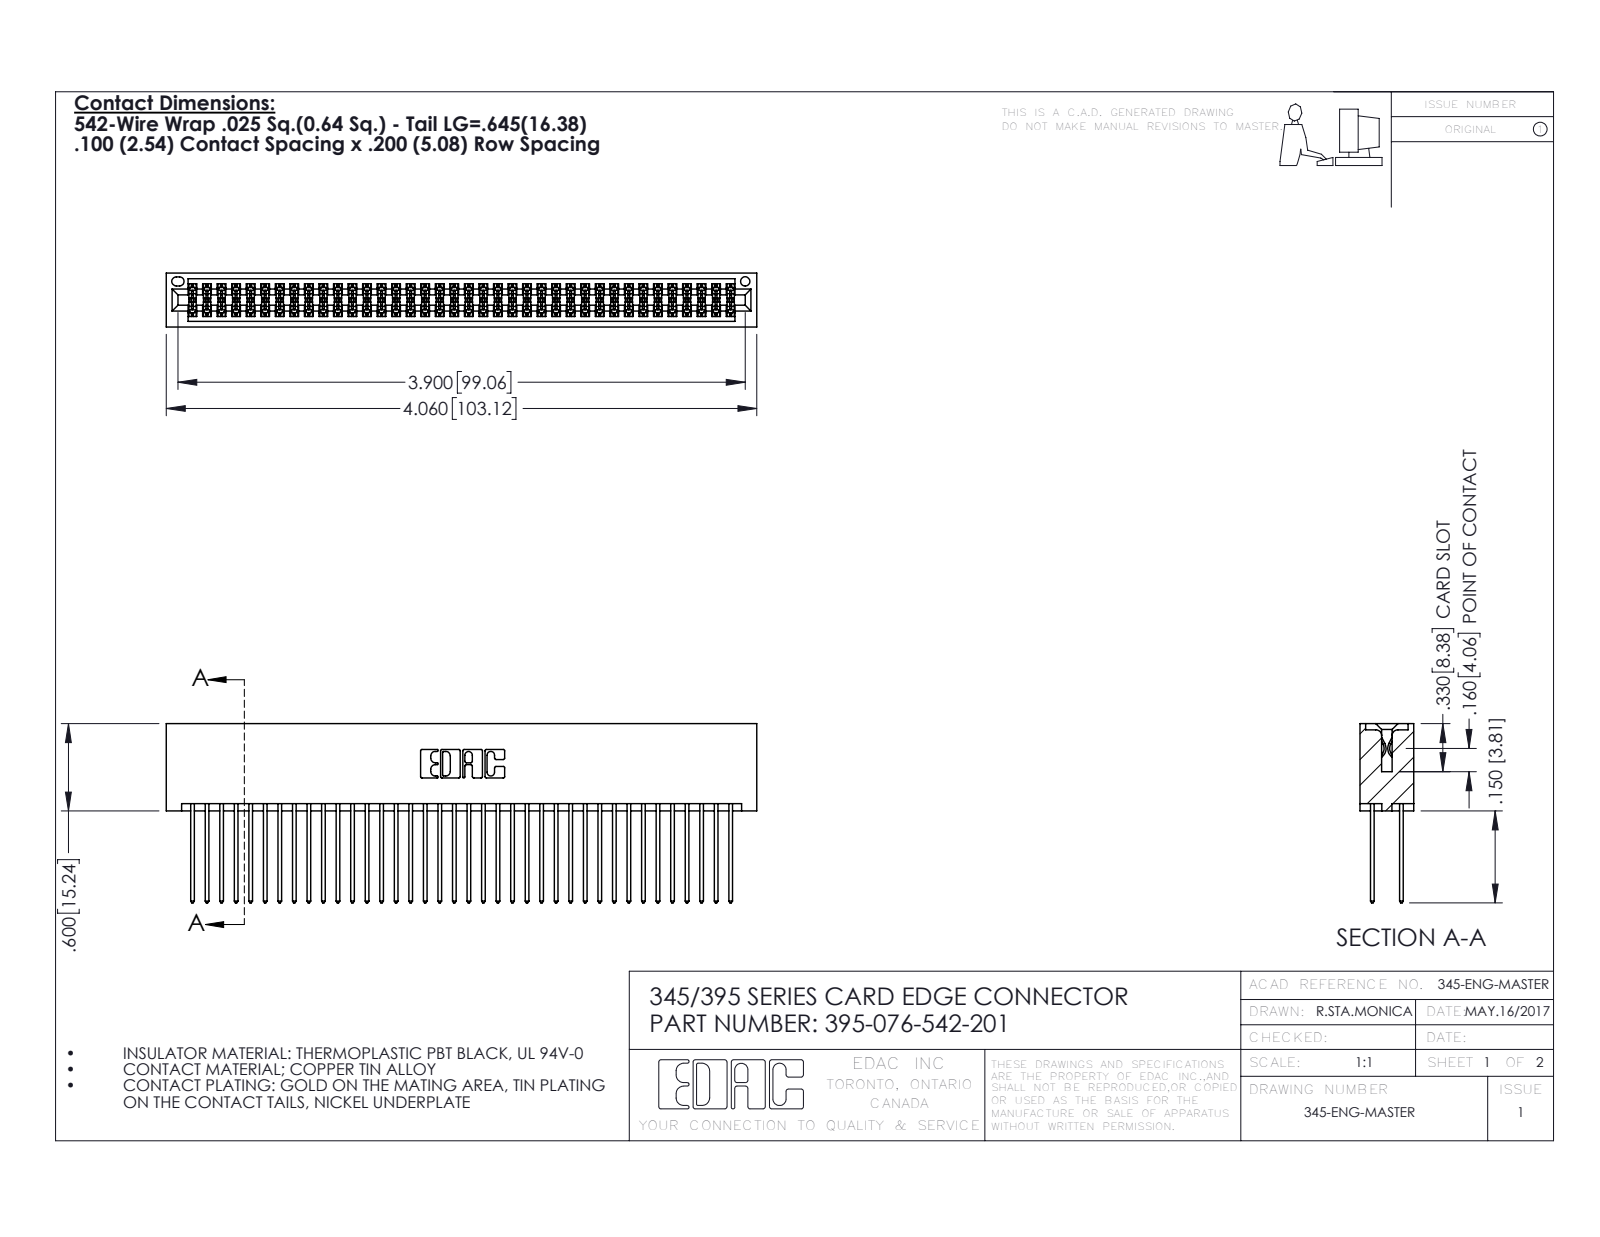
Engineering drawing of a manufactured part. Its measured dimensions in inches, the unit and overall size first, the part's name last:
Units: inches
Overall size (bounding box): 4.06 × 1.232 × 0.37
Round holes (diameter × count): ⌀0.064 ×1
Partial cylindrical surfaces — rounded edges, fillets, slot ends (radius × count): R0.006 ×114, R0.01 ×76, R0.01 ×22, R0.007 ×6, R0.031 ×6, R0.026 ×3, R0.014 ×2, R0.019 ×2
Main face-to-face distances: 0.298, 0.072, 0.2, 0.098, 0.272, 0.025, 0.225, 0.37, 0.175, 0.149
Volume: 0.668 in³ · Surface area: 28.01 in²
Bodies: 77 solids, 3918 faces (2584 planar, 1334 cylindrical, 0 other)
Part name (STEP PRODUCT): 345 Part_No Mounting Lugs; 395-076-542-201; 345-292-001_345-293-142
STEP written by: SolidWorks 2016 (CONFIG_CONTROL_DESIGN)
